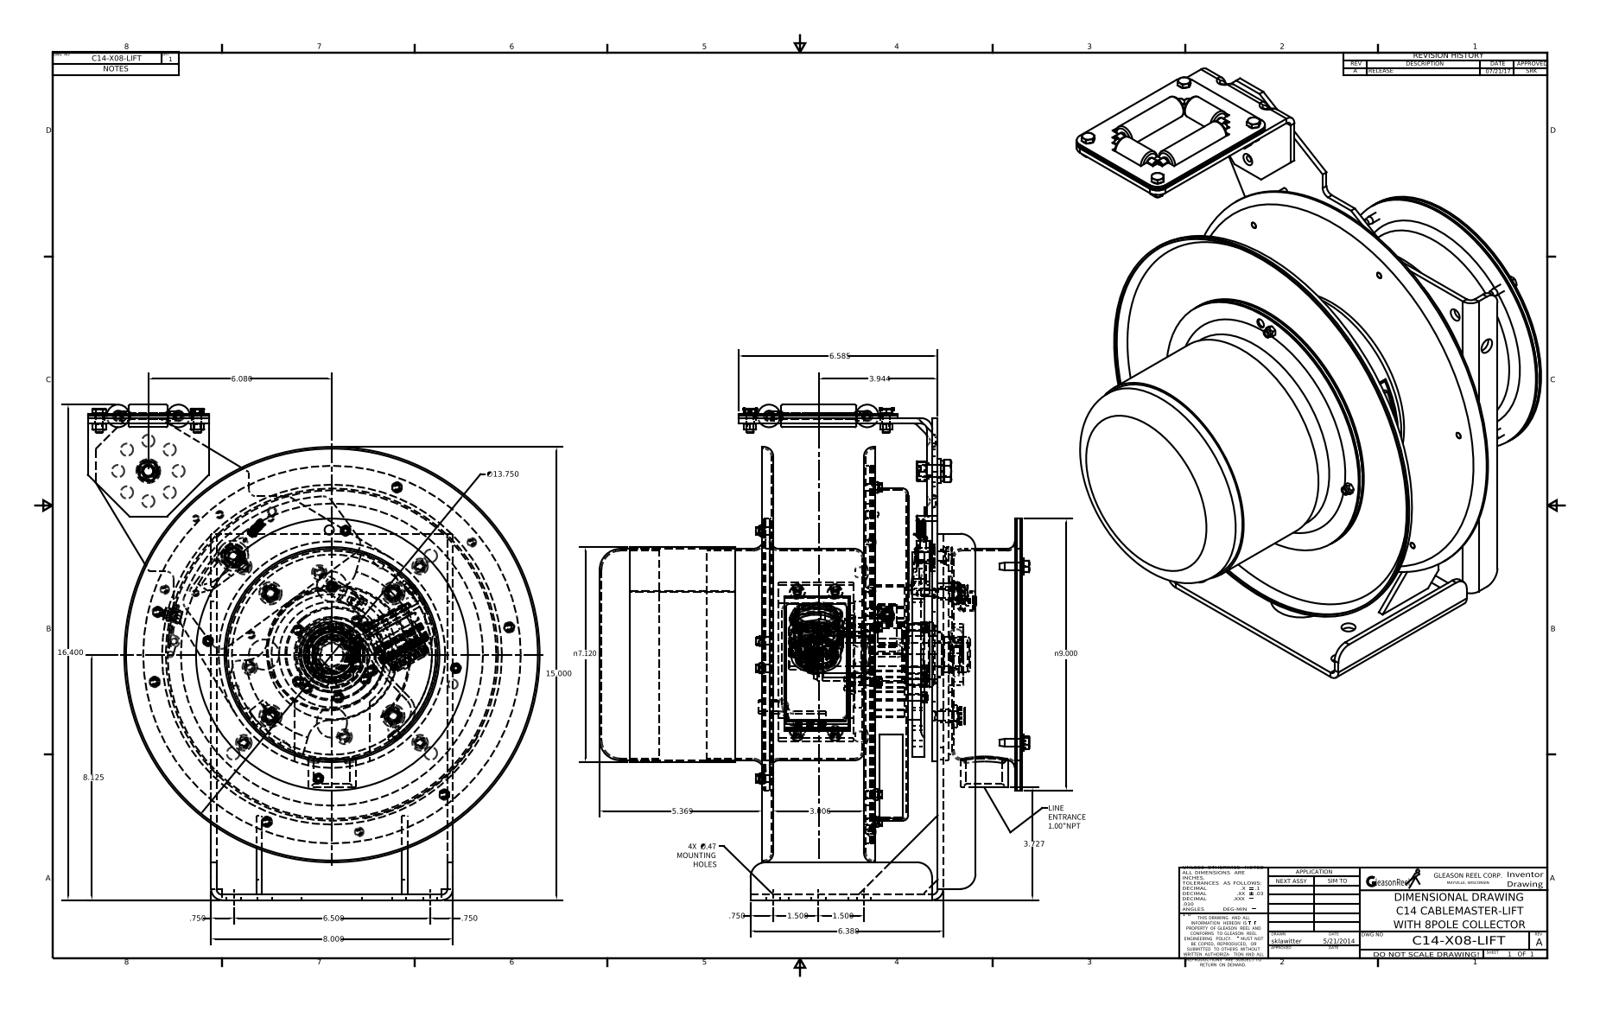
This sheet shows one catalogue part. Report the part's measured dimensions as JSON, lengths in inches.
{"part_name": "C14-X08-LIFT (SW)", "step_written_by": "Autodesk Inventor 2016 (AUTOMOTIVE_DESIGN)", "units": "inches", "bodies": {"solids": 159, "faces": 3187, "planar": 1260, "cylindrical": 1032, "other": 895}, "overall_size": [16.4, 14.955, 14.224], "volume_in3": 166.8, "surface_area_in2": 3618, "round_holes": [[0.25, 26], [0.197, 24], [0.163, 19], [0.406, 13], [0.219, 12], [0.213, 8], [0.42, 8], [0.47, 6], [1, 6], [0.194, 5], [0.281, 5], [0.314, 5]], "round_bosses_or_shafts": [[0.197, 24], [0.268, 10], [0.394, 7], [0.236, 6], [0.5, 5], [0.457, 5], [0.315, 5], [0.75, 4]], "partial_cylinders_radius": [[0.03, 67], [0.009, 64], [0.015, 58], [0.078, 18], [0.006, 16], [0.06, 12], [0.25, 8], [0.375, 8]], "face_to_face_distances": [0.06, 0.125, 0.244, 1.218, 4.991, 0.185, 0.059, 0.184, 0.179, 3.309], "hole_center_spacings": [5.933, 0.765, 1, 1.25, 1.414, 1.848, 2.044, 2.044]}
